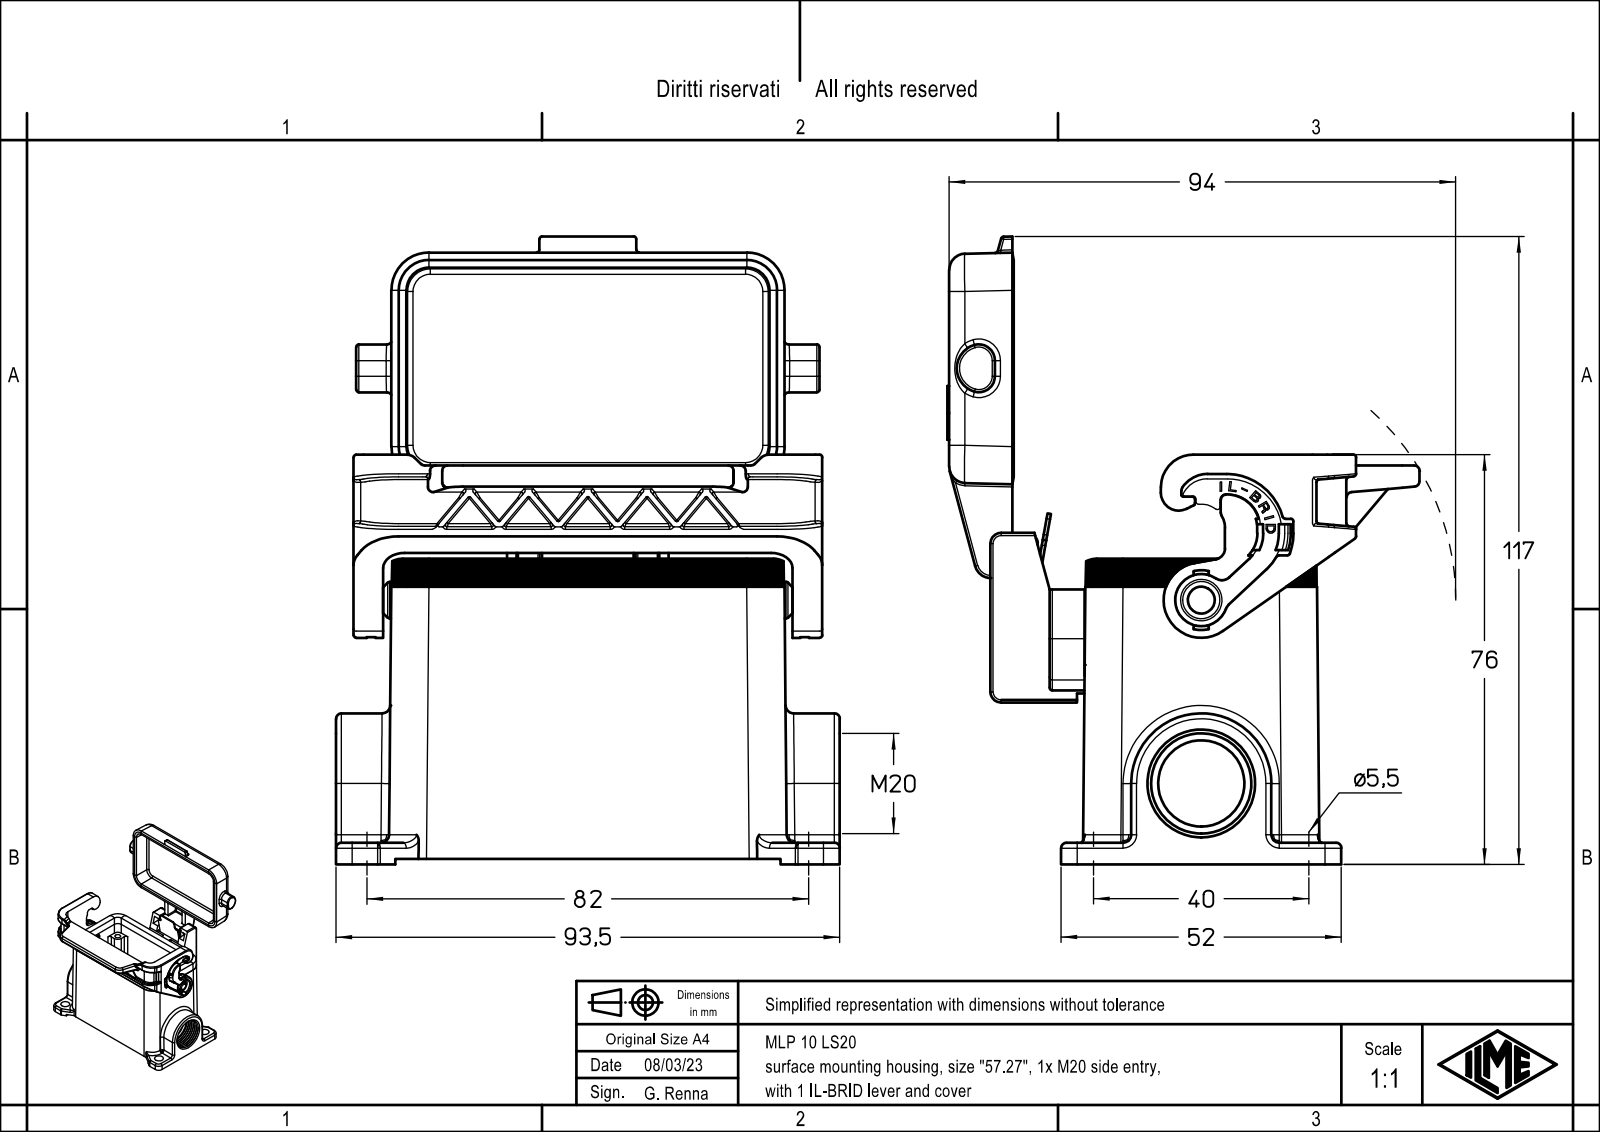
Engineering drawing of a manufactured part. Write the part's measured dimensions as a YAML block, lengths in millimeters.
part_name: "MLP 10 LS20"
step_written_by: "Creo Elements/Direct Modeling 20.1B 02-Apr-2019 (C) Parametric Technology GmbH (AUTOMOTIVE_DESIGN)"
units: millimeters
bodies: {solids: 1, faces: 1384, planar: 801, cylindrical: 416, other: 167}
overall_size: [116.49, 93.5, 87.8]
volume: 111326
surface_area: 63906
round_holes:
  - {diameter: 3, count: 4}
  - {diameter: 3.5, count: 4}
  - {diameter: 5, count: 4}
  - {diameter: 5.5, count: 4}
  - {diameter: 3.25, count: 1}
  - {diameter: 4.2, count: 1}
  - {diameter: 5.4, count: 1}
  - {diameter: 7.7, count: 1}
  - {diameter: 16, count: 1}
  - {diameter: 18.6, count: 1}
round_bosses_or_shafts:
  - {diameter: 8.4, count: 1}
  - {diameter: 6.9, count: 1}
  - {diameter: 6.8, count: 1}
  - {diameter: 5.2, count: 1}
  - {diameter: 4, count: 1}
  - {diameter: 3.2, count: 1}
partial_cylinders:
  - {radius: 0.5, count: 28}
  - {radius: 0.1, count: 27}
  - {radius: 1, count: 26}
  - {radius: 0.2, count: 23}
  - {radius: 3, count: 23}
  - {radius: 2, count: 20}
  - {radius: 1.5, count: 19}
  - {radius: 0.17, count: 17}
face_to_face_distances: [2, 3, 2.8, 1, 69.75, 71.75, 76, 4, 5.5, 81.5]
hole_center_spacings: [2.92, 11.7, 14.09, 29.54, 35.76, 37.64, 58.55, 65.52]
